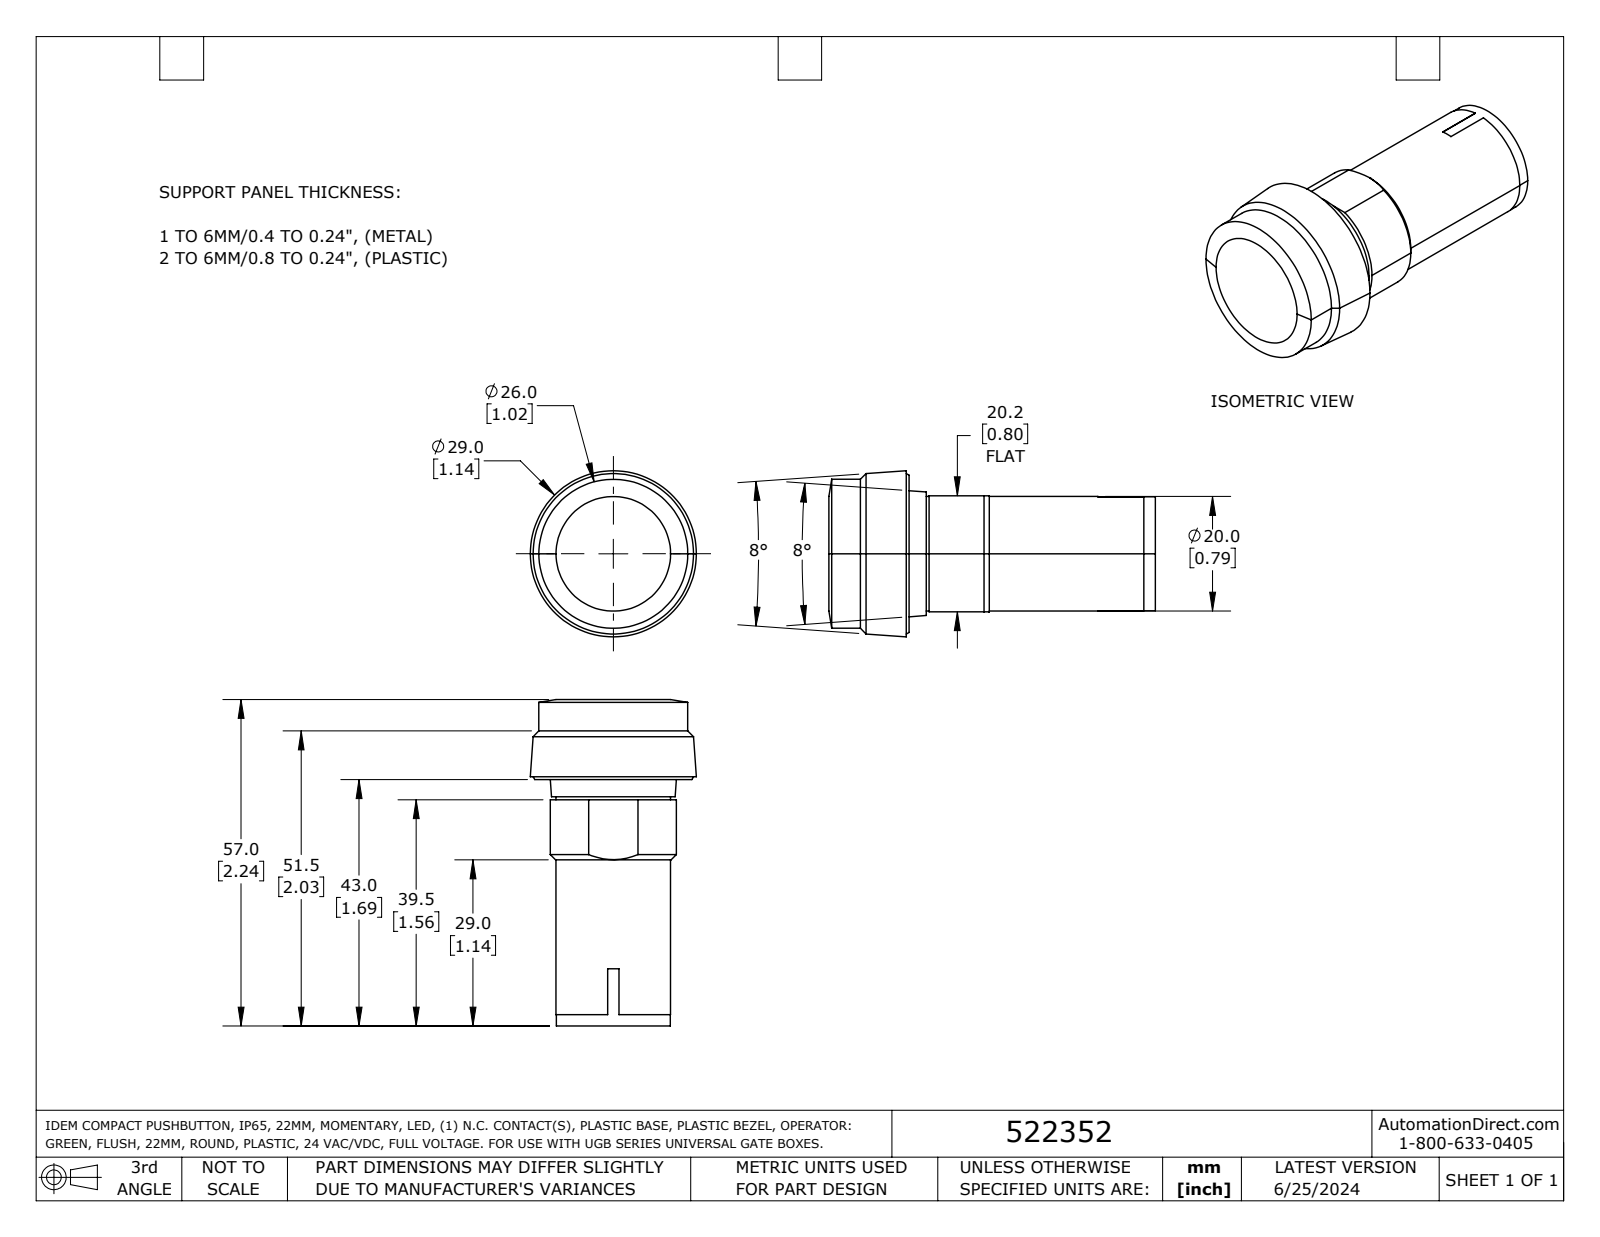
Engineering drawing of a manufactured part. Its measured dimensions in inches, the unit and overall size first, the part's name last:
Units: inches
Overall size (bounding box): 2.244 × 1.142 × 1.142
Round bosses / shafts (diameter × count): ⌀1.024 ×1, ⌀0.787 ×1, ⌀0.783 ×1
Partial cylindrical surfaces — rounded edges, fillets, slot ends (radius × count): R0.433 ×1
Main face-to-face distances: 2.244, 0.551, 1.693, 0.138, 0.02, 0.797, 0.689, 1.555, 0.669, 0.118
Volume: 1.37 in³ · Surface area: 8.094 in²
Bodies: 1 solid, 41 faces (17 planar, 12 cylindrical, 12 other)
Part name (STEP PRODUCT): 522352
STEP written by: SolidWorks 2023 (AUTOMOTIVE_DESIGN)
